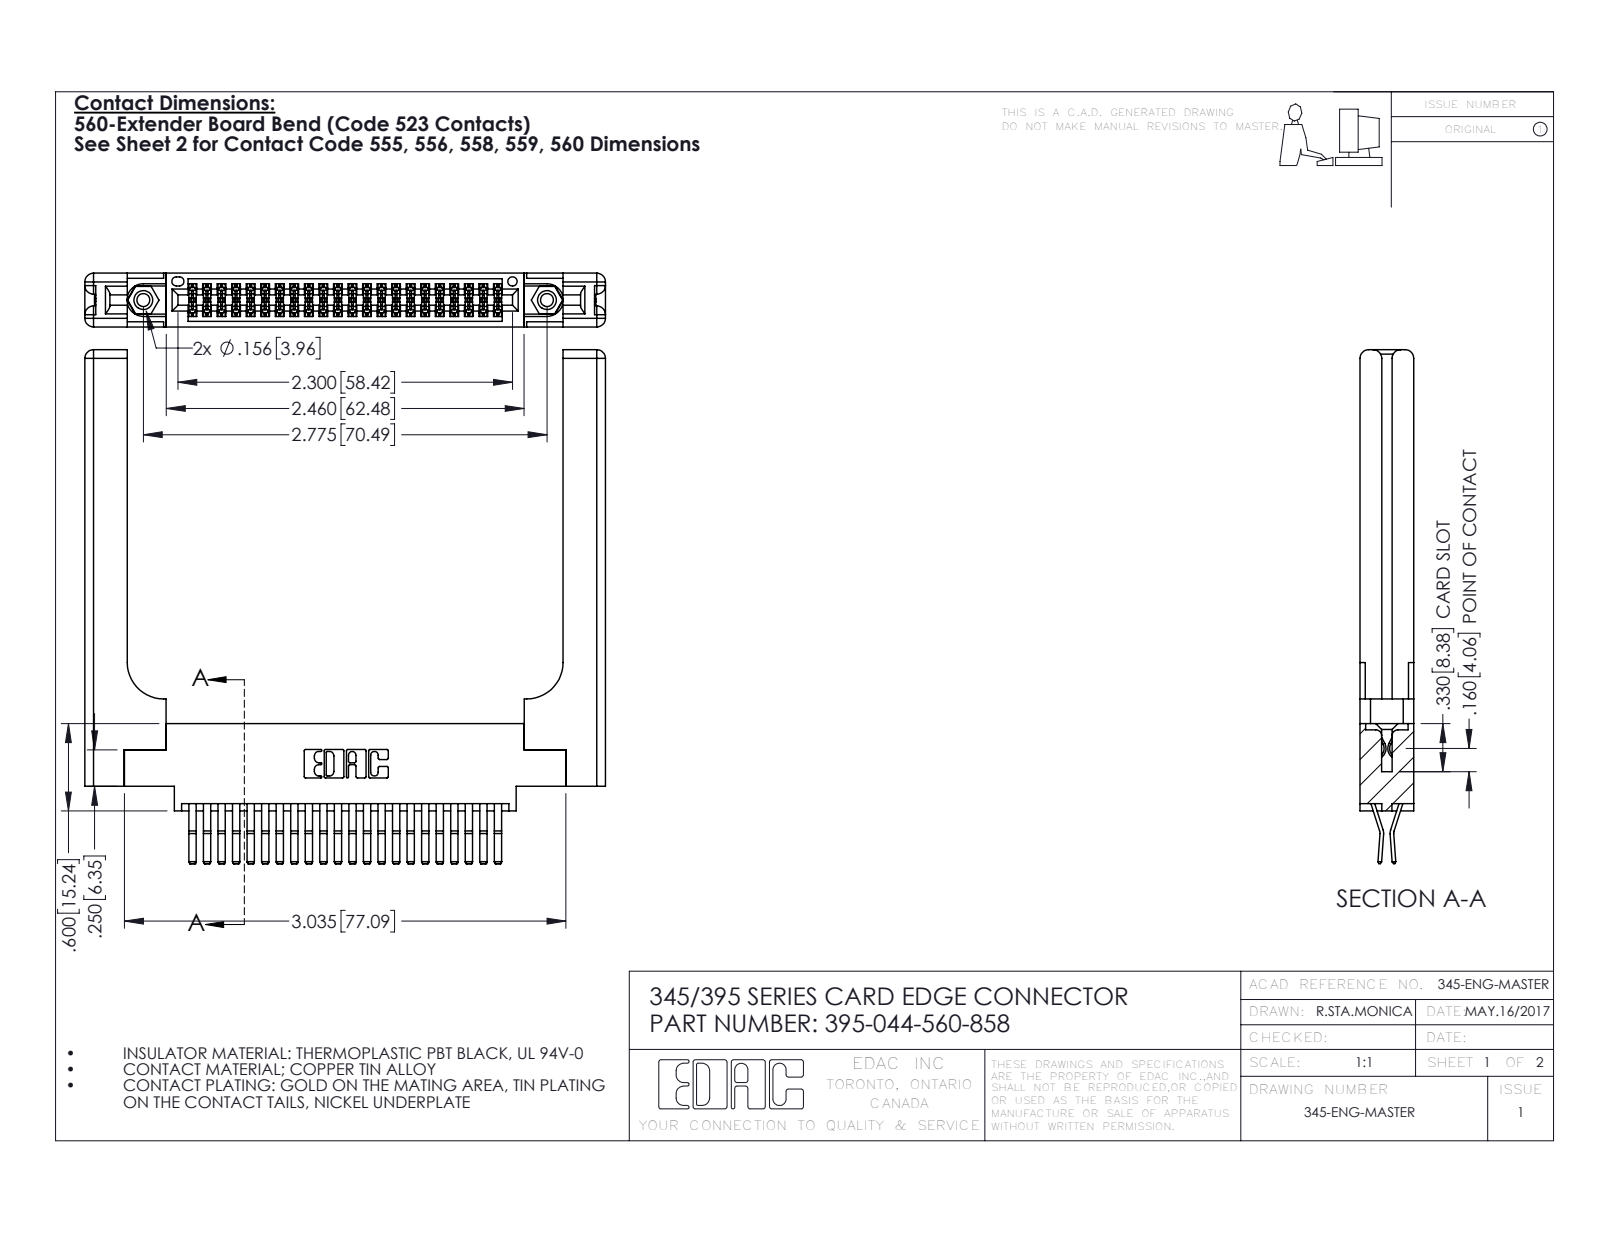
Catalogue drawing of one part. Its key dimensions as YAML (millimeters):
part_name: "345-292-001_560 Tail; 345 Part_0.170 Offset - 0.156 Dia-TH; 345-250-001_345-250-001-102; 345-220-058_345-220-058 (+1 more)"
step_written_by: "SolidWorks 2016 (CONFIG_CONTROL_DESIGN)"
units: millimeters
bodies: {solids: 49, faces: 2674, planar: 1684, cylindrical: 930, other: 60}
overall_size: [90.9, 89.7, 9.4]
volume: 17290
surface_area: 18590
round_holes:
  - {diameter: 2.3, count: 2}
  - {diameter: 3.2, count: 2}
  - {diameter: 4, count: 2}
  - {diameter: 1.6, count: 1}
round_bosses_or_shafts:
  - {diameter: 3.9, count: 2}
partial_cylinders:
  - {radius: 0.2, count: 67}
  - {radius: 0.3, count: 22}
  - {radius: 1.5, count: 16}
  - {radius: 0.2, count: 6}
  - {radius: 0.8, count: 6}
  - {radius: 0.7, count: 3}
  - {radius: 0.3, count: 2}
  - {radius: 0.4, count: 2}
face_to_face_distances: [9.4, 1.8, 7.6, 0.6, 3.8, 3.8, 2, 5.7, 5.6, 3.1]
hole_center_spacings: [6.9, 64.5, 70.5]
